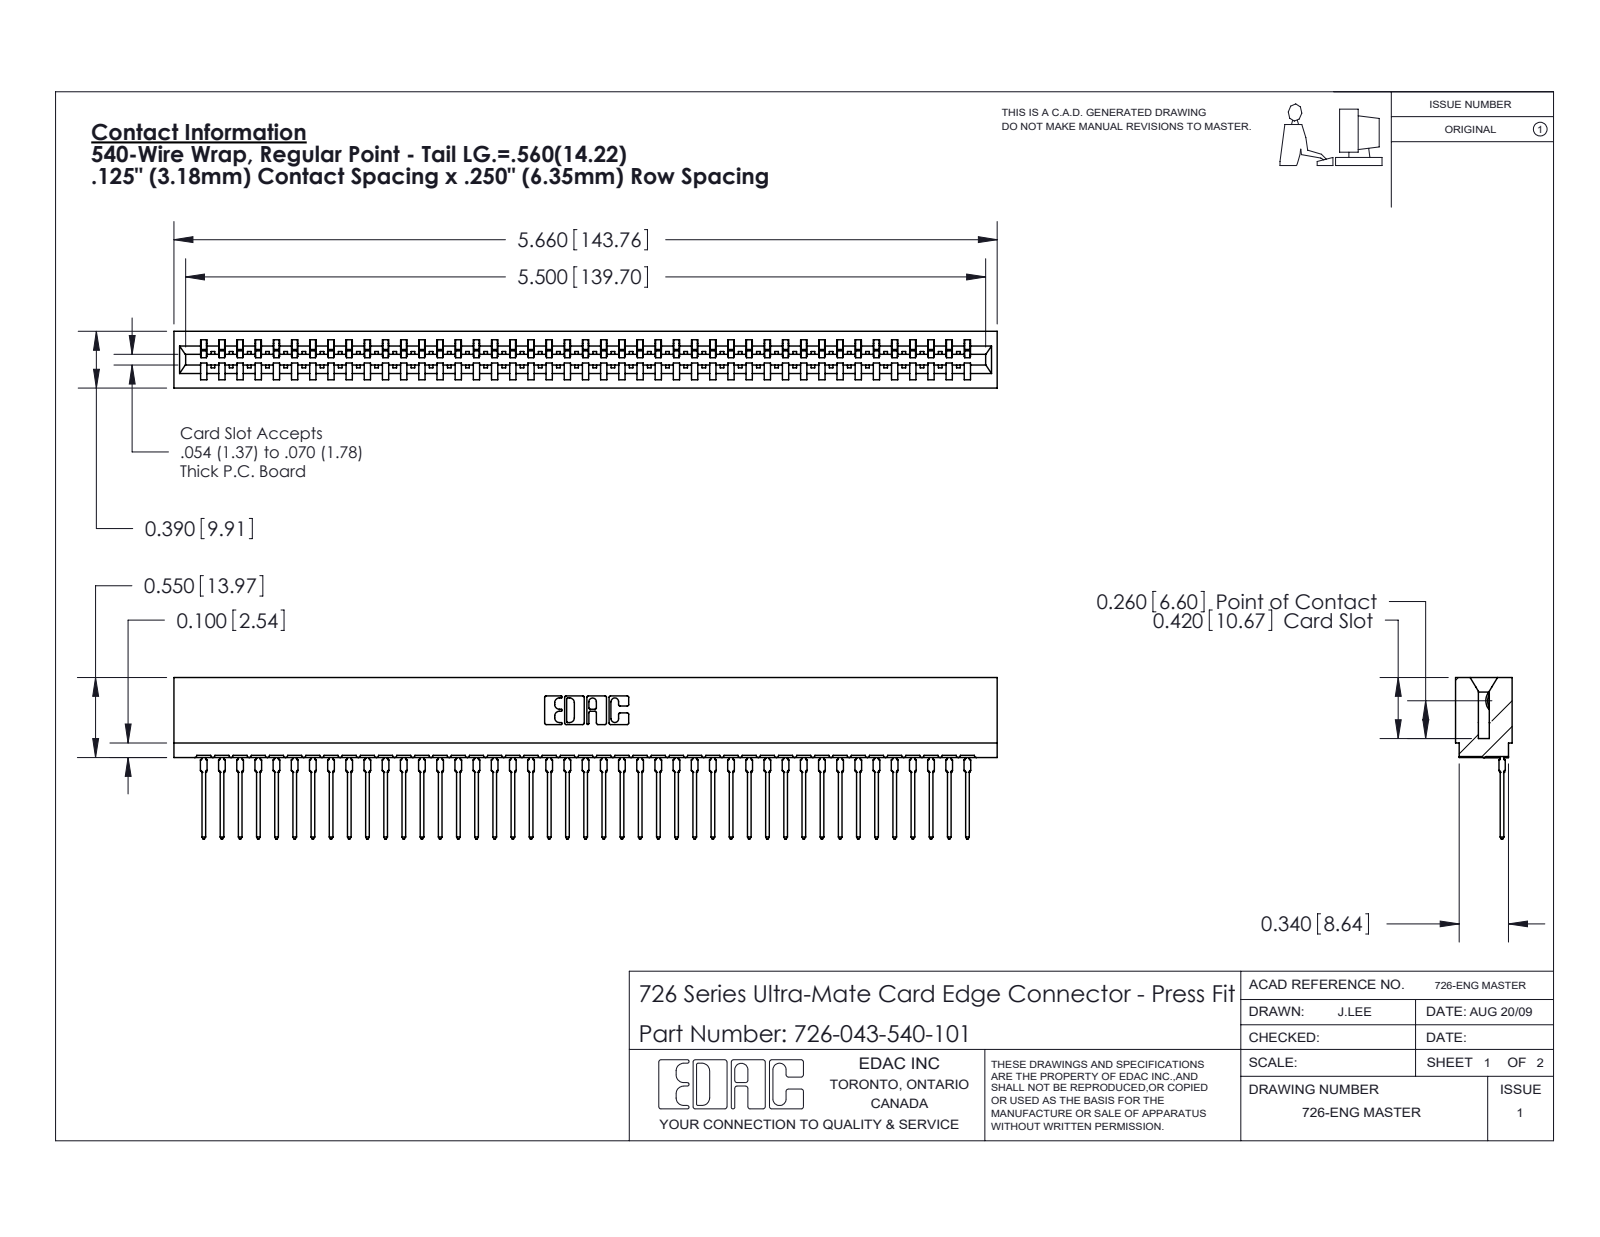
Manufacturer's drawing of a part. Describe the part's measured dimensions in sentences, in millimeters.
The part is named "726-043-540-101; 746-292-001_540; 726 Part_.515 Slot Depth - 01". Its 3-D file was written by "SolidWorks 2020 (CONFIG_CONTROL_DESIGN)". It is 44 solids with 4741 faces: 2764 planar, 859 cylindrical and 1118 other. Overall it measures 143.8 by 28.2 by 9.9 millimeters. Its volume is 12 900 cubic millimeters and its surface area 20 260 square millimeters. Partial cylindrical surfaces (rounded edges, fillets, slot ends): 86 of radius 0.5, 44 of radius 0.4, 22 of radius 0.3, 6 of radius 0.2, 6 of radius 0.8, 4 of radius 0.1, 4 of radius 0.3, 3 of radius 0.7. The main face-to-face distances are 1.4, 8.5, 9.9, 0.6, 7.8, 6.4, 2.1, 7, 9.3, 0.8.
